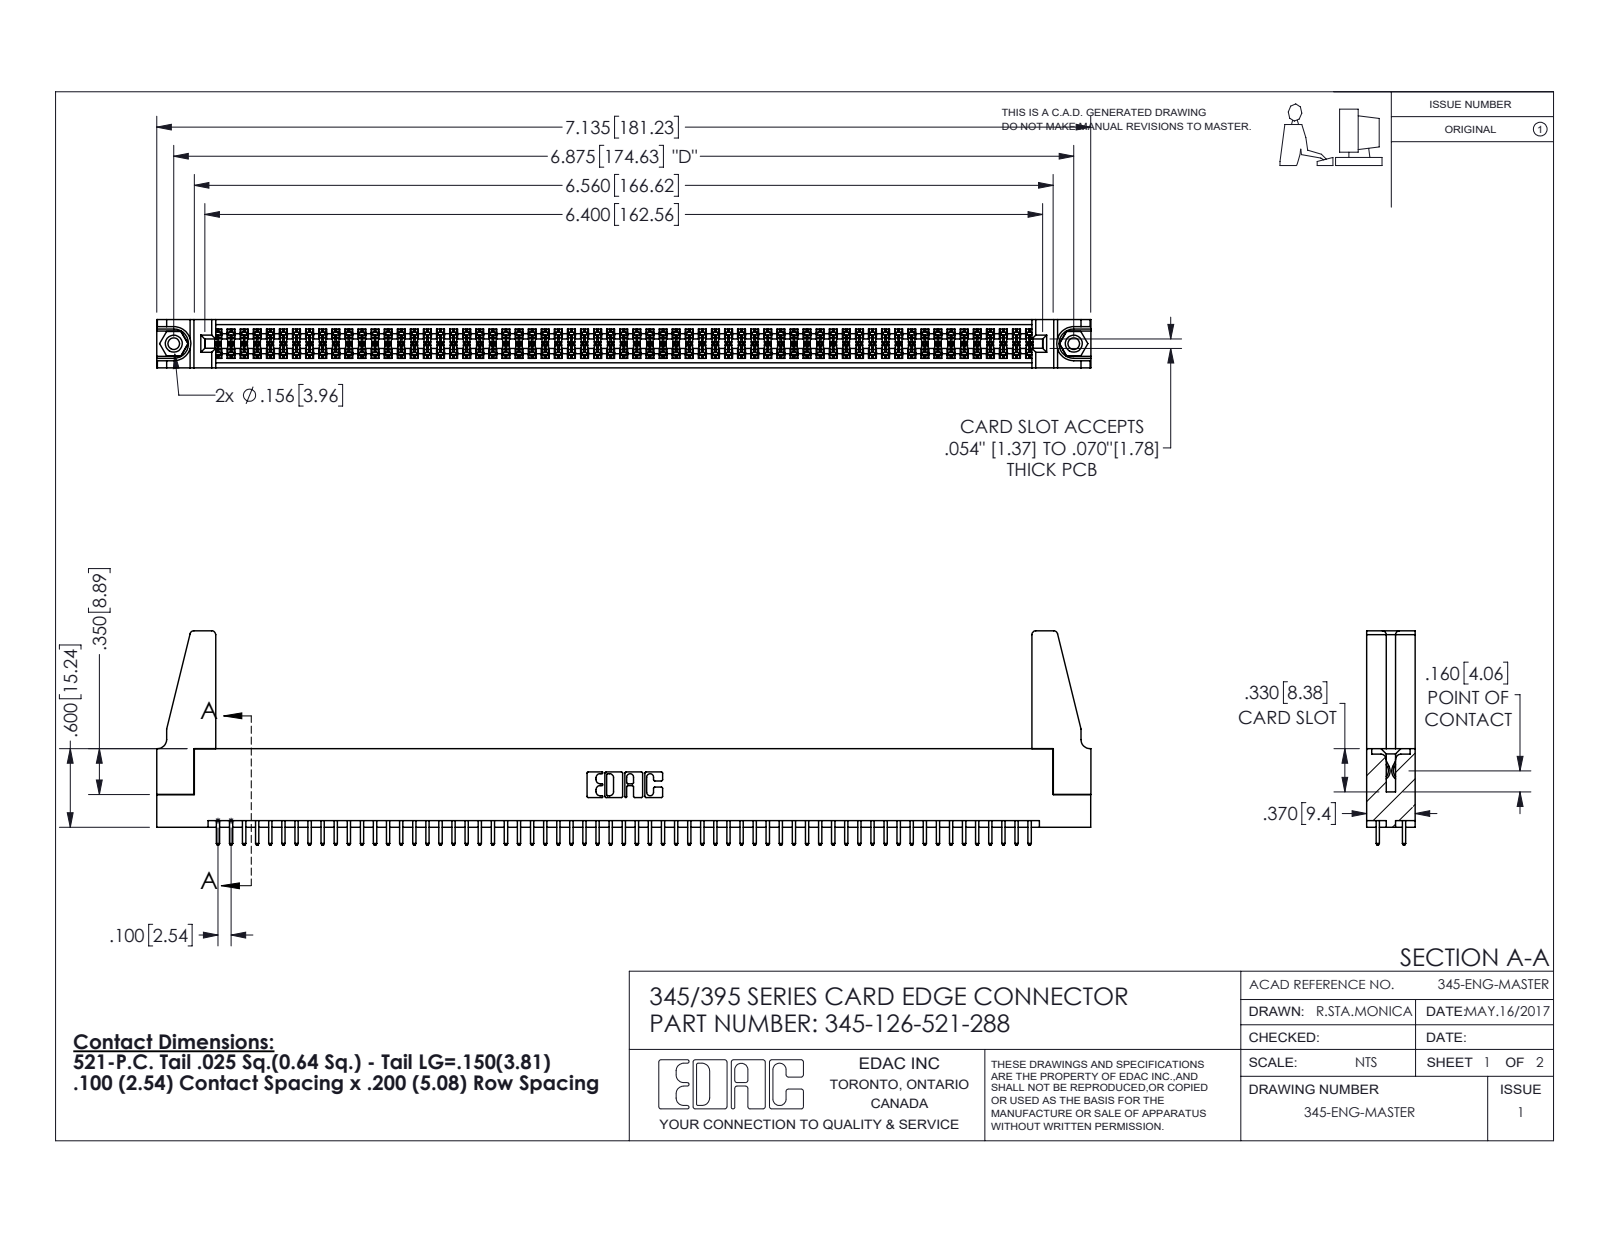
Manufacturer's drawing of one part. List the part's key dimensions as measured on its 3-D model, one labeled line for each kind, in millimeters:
Part name (STEP PRODUCT): 345 Part_Flush Mounting Lugs - 0.156 Dia-TH; 345-220-078_345-220-088; 345-292-001_345-293-121; 345-250-001_345-250-001-102 (+1 more)
STEP written by: SolidWorks 2016 (CONFIG_CONTROL_DESIGN)
Units: millimetres
Bodies: 131 solids, 6550 faces (4310 planar, 2224 cylindrical, 16 other)
Overall size (bounding box): 181.3 × 41.6 × 9.4
Volume: 21 010 mm³ · Surface area: 29 430 mm²
Round holes (diameter × count): ⌀2.3 ×2, ⌀3.2 ×2, ⌀4 ×2, ⌀1.6 ×1
Round bosses / shafts (diameter × count): ⌀3.9 ×2
Partial cylindrical surfaces — rounded edges, fillets, slot ends (radius × count): R0.2 ×189, R0.3 ×126, R0.3 ×22, R0.8 ×8, R0.2 ×6, R0.8 ×6, R0.7 ×3, R0.4 ×2
Main face-to-face distances: 1.8, 7.6, 9.4, 5.1, 2.5, 6.9, 0.6, 5.7, 4.4, 3.8
Hole centre spacings: 6.9, 168.6, 174.6
